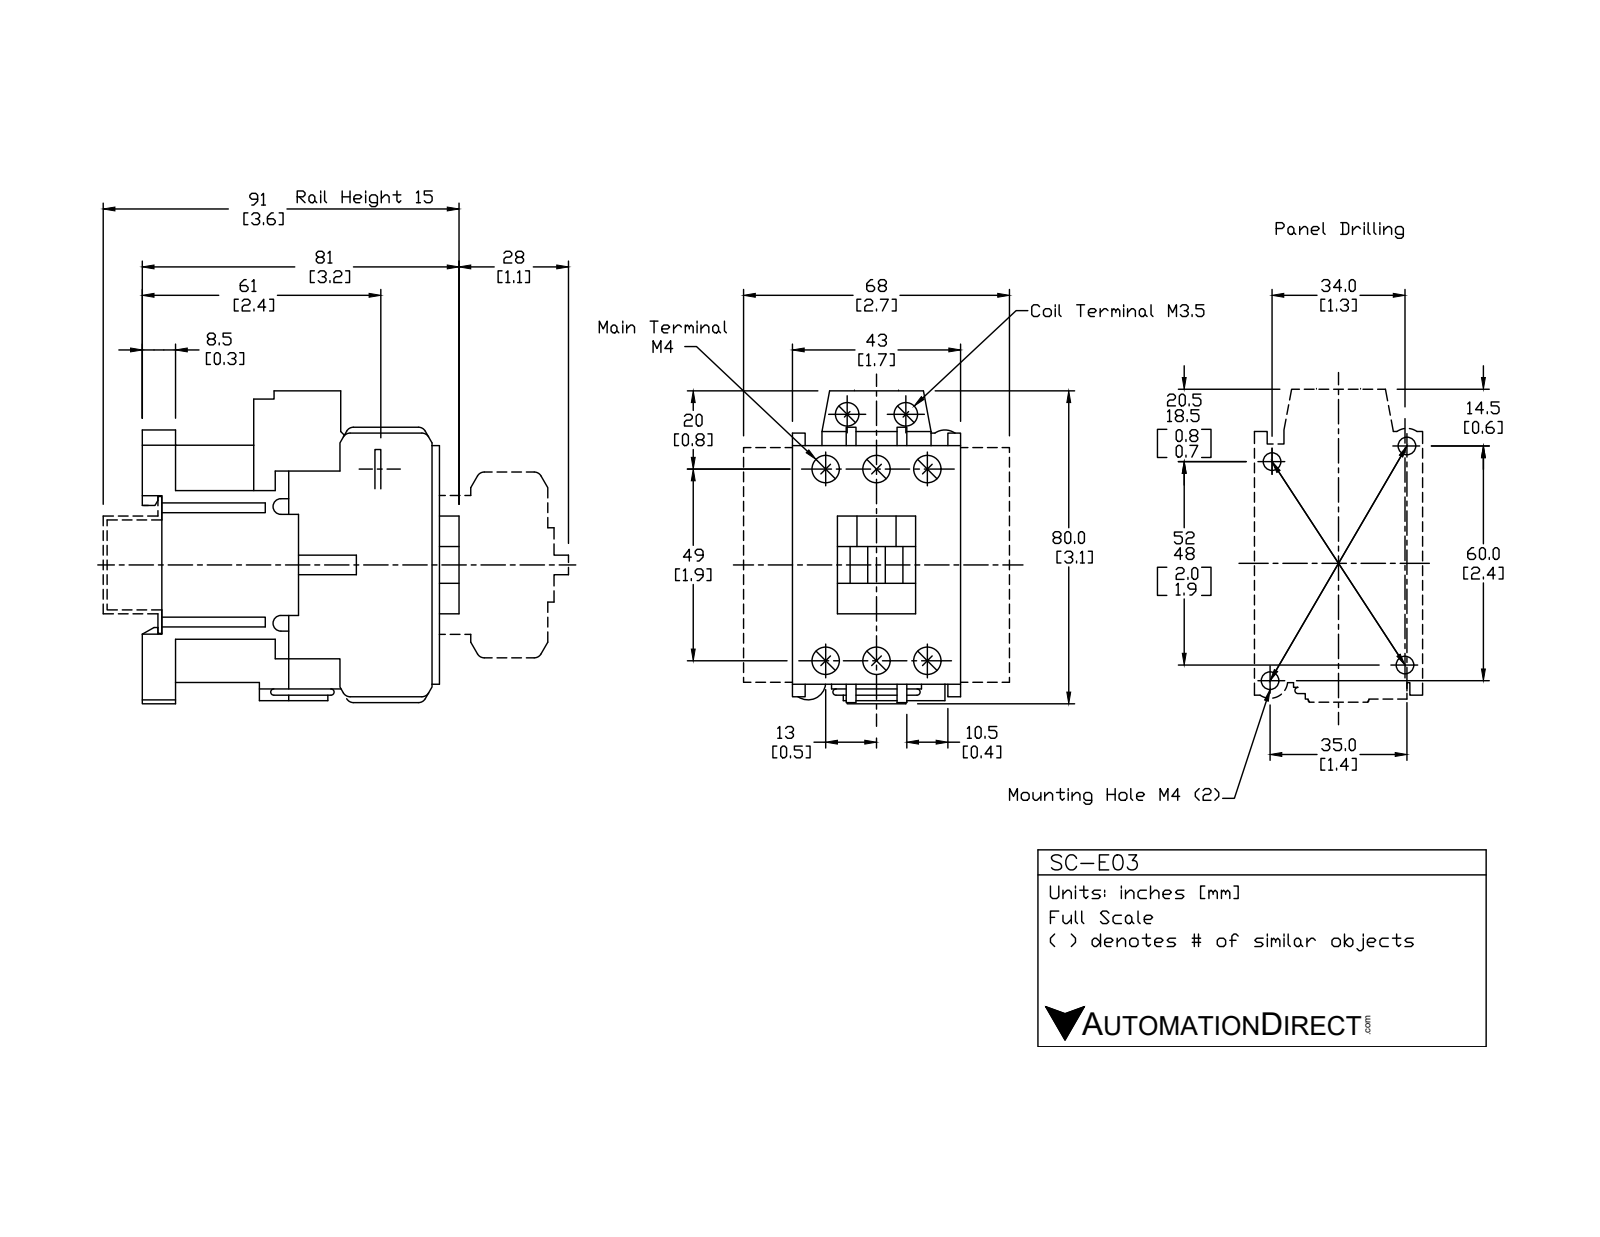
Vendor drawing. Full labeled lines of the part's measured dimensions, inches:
Part name (STEP PRODUCT): SC-E03-110VAC
STEP written by: SolidWorks 2015 (AUTOMOTIVE_DESIGN)
Units: inches
Bodies: 1 solid, 1388 faces (1148 planar, 192 cylindrical, 48 other)
Overall size (bounding box): 3.189 × 3.189 × 1.693
Volume: 9.981 in³ · Surface area: 65.66 in²
Round holes (diameter × count): ⌀0.161 ×6, ⌀0.276 ×6, ⌀0.142 ×2, ⌀0.177 ×2, ⌀0.264 ×2, ⌀0.063 ×1
Round bosses / shafts (diameter × count): ⌀0.299 ×6, ⌀0.157 ×6, ⌀0.28 ×2, ⌀0.26 ×2, ⌀0.138 ×2
Partial cylindrical surfaces — rounded edges, fillets, slot ends (radius × count): R0.059 ×32, R0.079 ×14, R0.02 ×10, R0.024 ×4, R0.089 ×4, R0.14 ×4, R0.163 ×2, R0.177 ×2
Main face-to-face distances: 1.693, 0.512, 0.413, 0.098, 0.925, 1.299, 0.64, 1.053, 0.61, 0.541
Hole centre spacings: 0.512, 1.996, 1.929, 0.28, 0.301, 0.592, 0.625, 0.709
